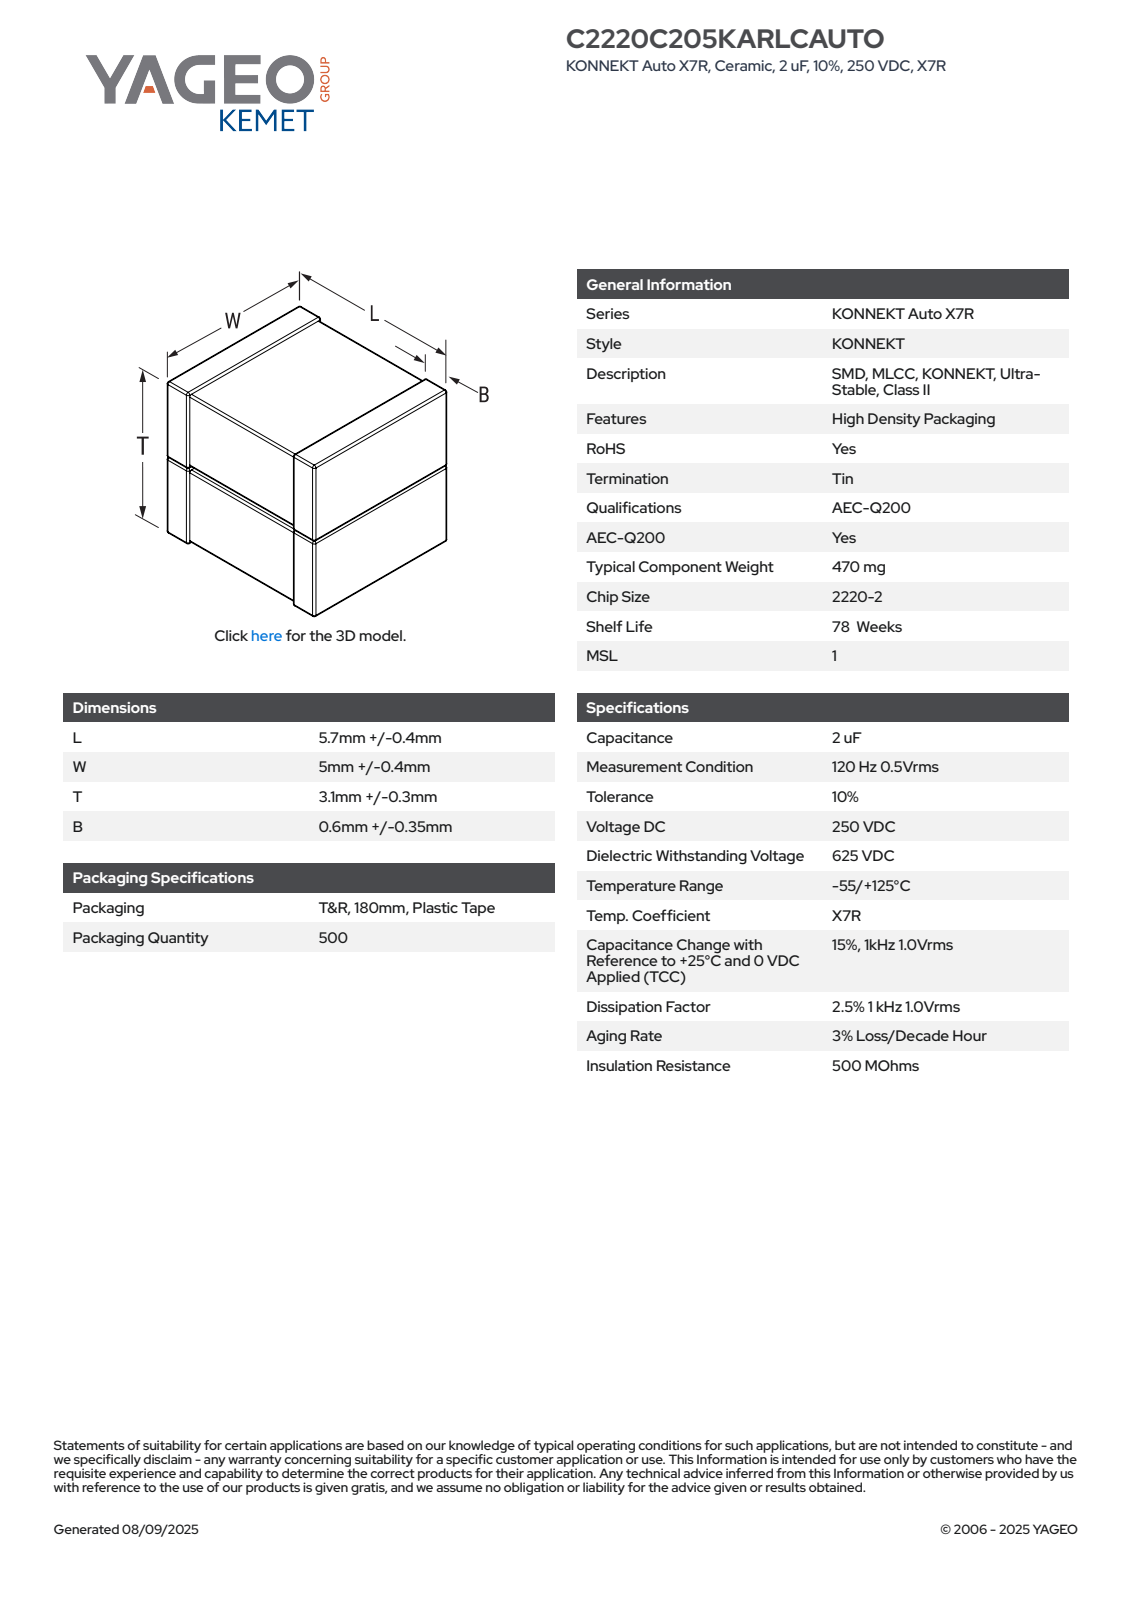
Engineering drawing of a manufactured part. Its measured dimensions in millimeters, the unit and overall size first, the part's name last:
Units: millimetres
Overall size (bounding box): 6.1 × 5.4 × 3.4
Main face-to-face distances: 1.56, 1.7, 3.26, 1.63, 1.77, 3.33, 6.1, 5.26, 5.33, 3.4
Volume: 104 mm³ · Surface area: 190 mm²
Bodies: 4 solids, 189 faces (81 planar, 76 cylindrical, 32 other)
Part name (STEP PRODUCT): CCSS_K2T_2220-2_L6.1W5.4B0.95T3.4
STEP written by: SolidWorks 2020 (AUTOMOTIVE_DESIGN)
